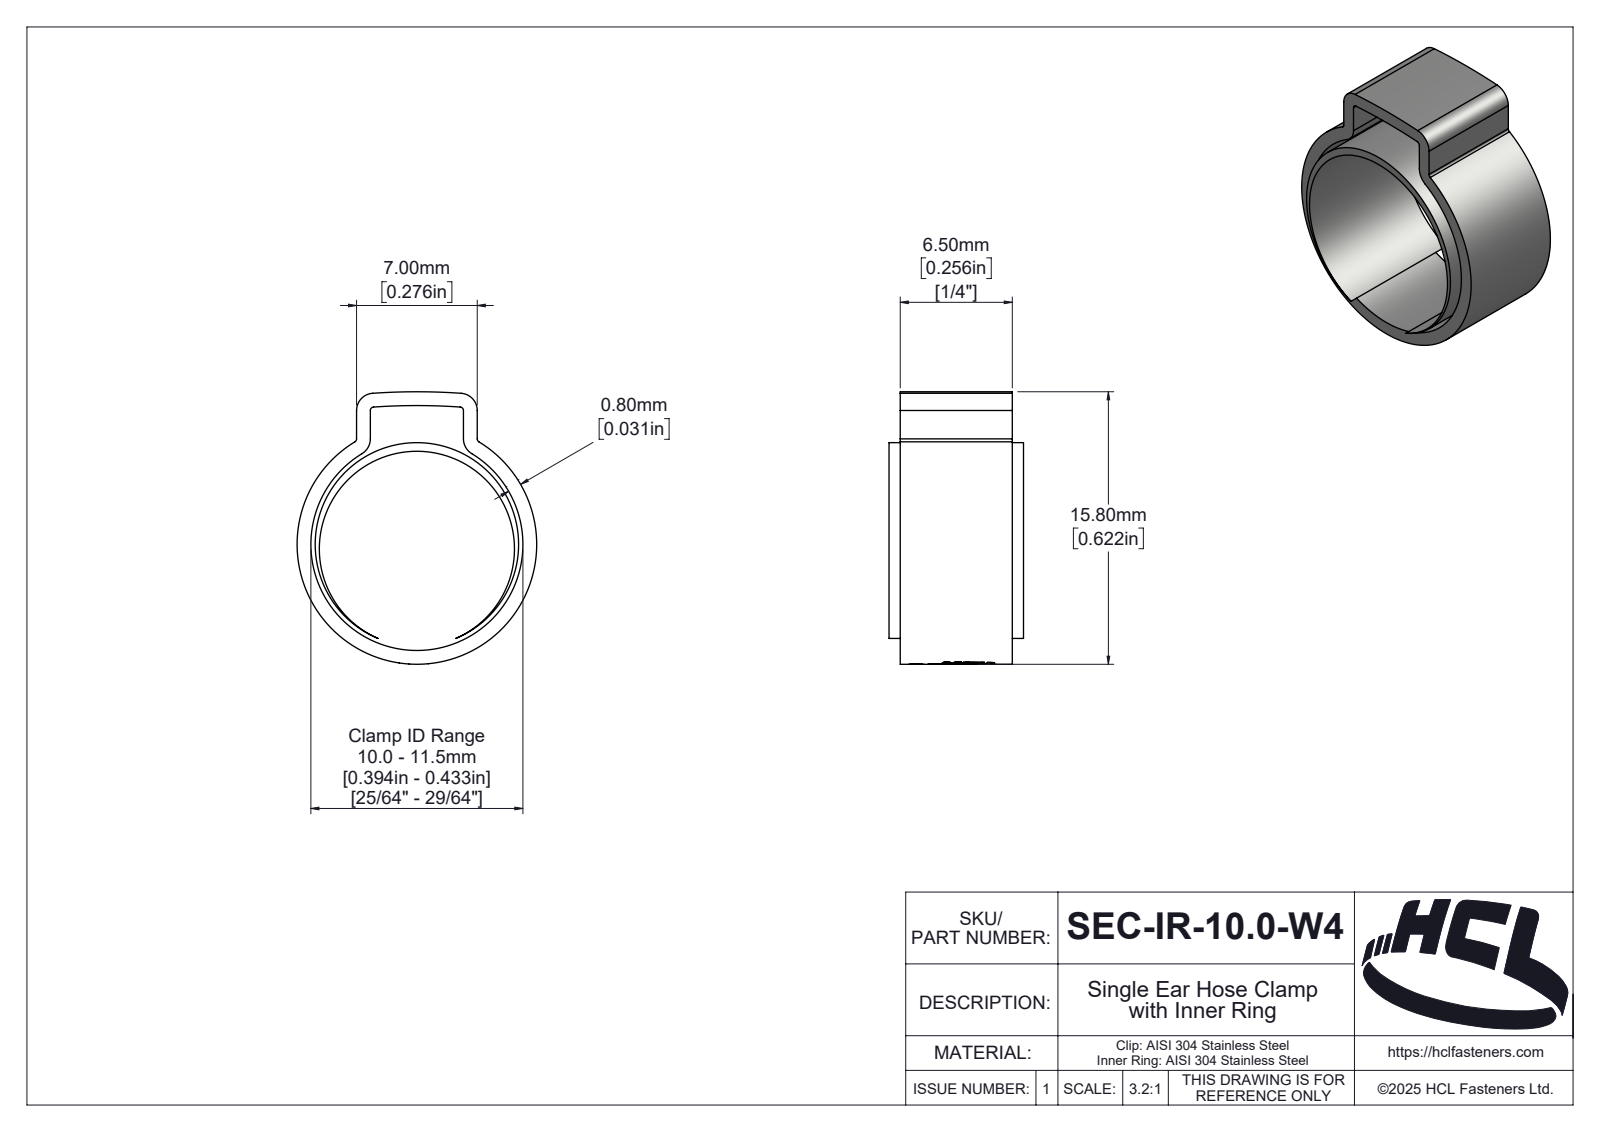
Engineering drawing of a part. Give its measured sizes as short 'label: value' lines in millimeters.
name: SEC-IR-10.0-W4
written by: SolidWorks 2025 (AUTOMOTIVE_DESIGN)
unit: mm
bodies: 2 solids, 131 faces (10 planar, 72 cylindrical, 49 other)
size: 15.8 × 13.9 × 7.8
volume: 304 mm³; area: 1 179 mm²
holes: 1× ⌀11.32, 1× ⌀12.3
bosses: 1× ⌀13.9, 1× ⌀11.8
rounds: 4× R0.2, 4× R1, 1× R0.21, 1× R0.88, 1× R1.09, 1× R1.15, 1× R1.39, 1× R1.97
face distances: 6.5, 0.8, 6.2, 0.65, 7.15, 7, 5.4, 7.8, 3.21, 2.41
